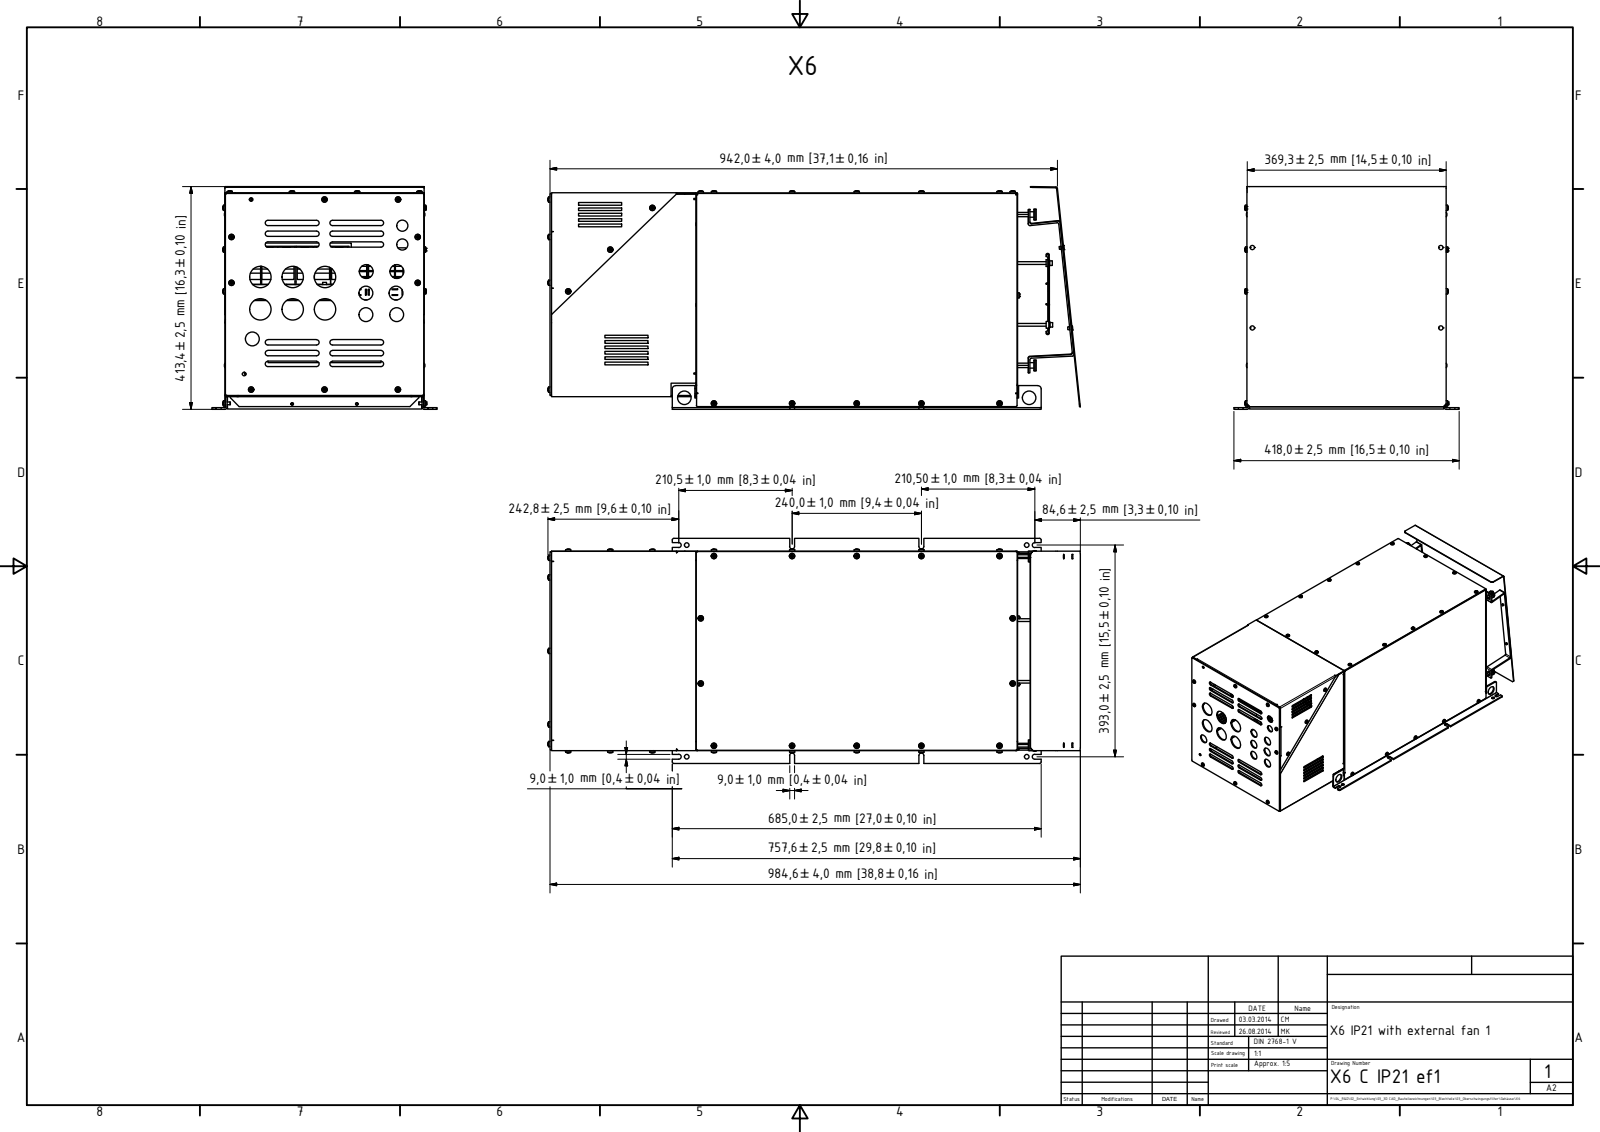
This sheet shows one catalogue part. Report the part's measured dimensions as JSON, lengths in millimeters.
{"part_name": "10100398 Deckel X5_X6; 10100402 Seitenwand X6; 10100400 Anschlussblech X6; 10100401 Lüfterblech X6 (+8 more)", "step_written_by": "Autodesk Inventor 2015 (AUTOMOTIVE_DESIGN)", "units": "millimeters", "bodies": {"solids": 152, "faces": 10274, "planar": 6130, "cylindrical": 2430, "other": 1714}, "overall_size": [988.42, 418, 413.43], "volume_mm3": 4690000, "surface_area_mm2": 4931000, "round_holes": [[4.13, 40], [6.5, 38], [4, 13], [8.25, 12], [7, 9], [6, 8], [9, 8], [3.24, 7], [25.5, 7], [8.5, 6], [40, 6], [4.5, 4]], "round_bosses_or_shafts": [[5, 43], [4.6, 41], [8, 18], [18, 12], [1.4, 8], [4, 7], [10, 6], [8.5, 5]], "partial_cylinders_radius": [[0.23, 112], [1, 77], [0.5, 64], [0.15, 54], [2, 54], [5, 52], [3, 43], [0.1, 37]], "face_to_face_distances": [1, 2, 369, 368, 3, 370, 375, 377, 596, 378], "hole_center_spacings": [21, 120, 350, 352, 36.37, 145, 265, 385]}
